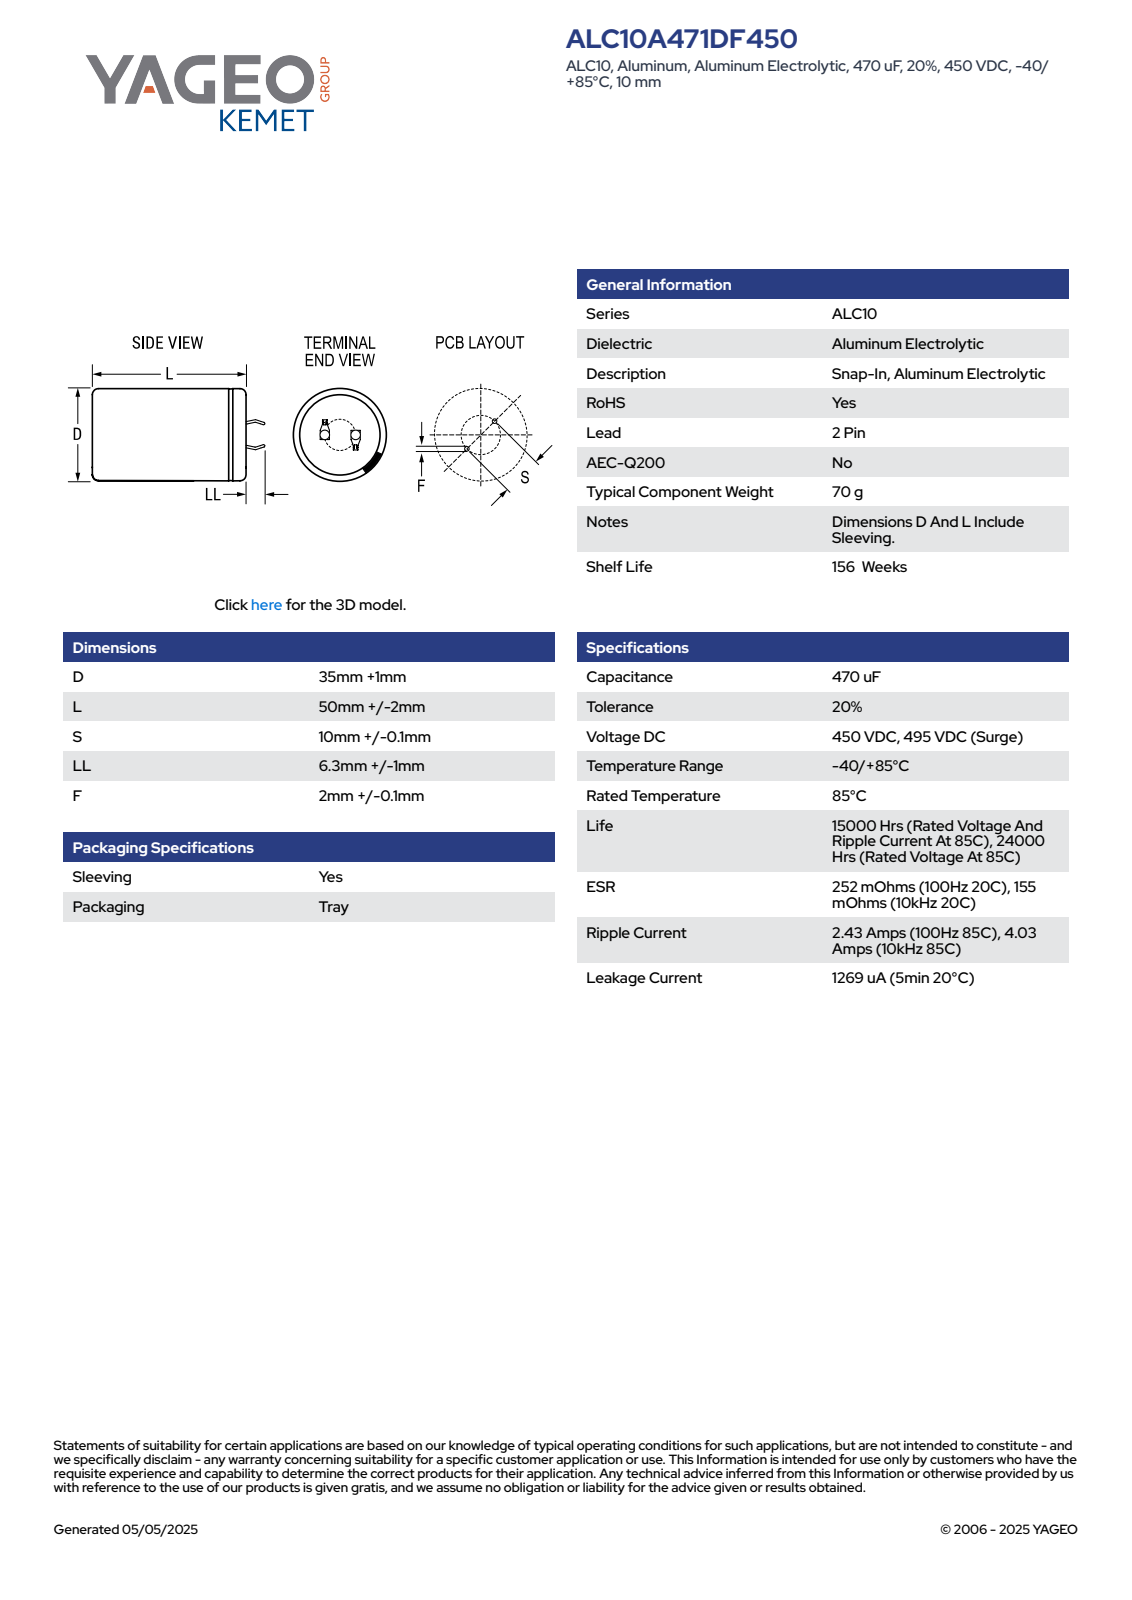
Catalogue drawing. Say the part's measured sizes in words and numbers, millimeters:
The part is named "CARS_K2P_35X50_D36L52S10LL7.3F2.1". Its 3-D file was written by "SolidWorks 2014 (AUTOMOTIVE_DESIGN)". It is 1 solid with 100 faces: 52 planar, 9 cylindrical and 39 other. Overall it measures 59.29 by 36 by 36 millimeters. Its volume is 52 401 cubic millimeters and its surface area 7 914 square millimeters. Round holes: 1 of diameter 31.85. Round bosses or shafts: 1 of diameter 36. Partial cylindrical surfaces (rounded edges, fillets, slot ends): 1 of radius 17.99. The main face-to-face distances are 51.99, 0.6, 52.49, 0.5, 7.08, 7.64, 0.75, 1.35, 7.68, 6.48.
